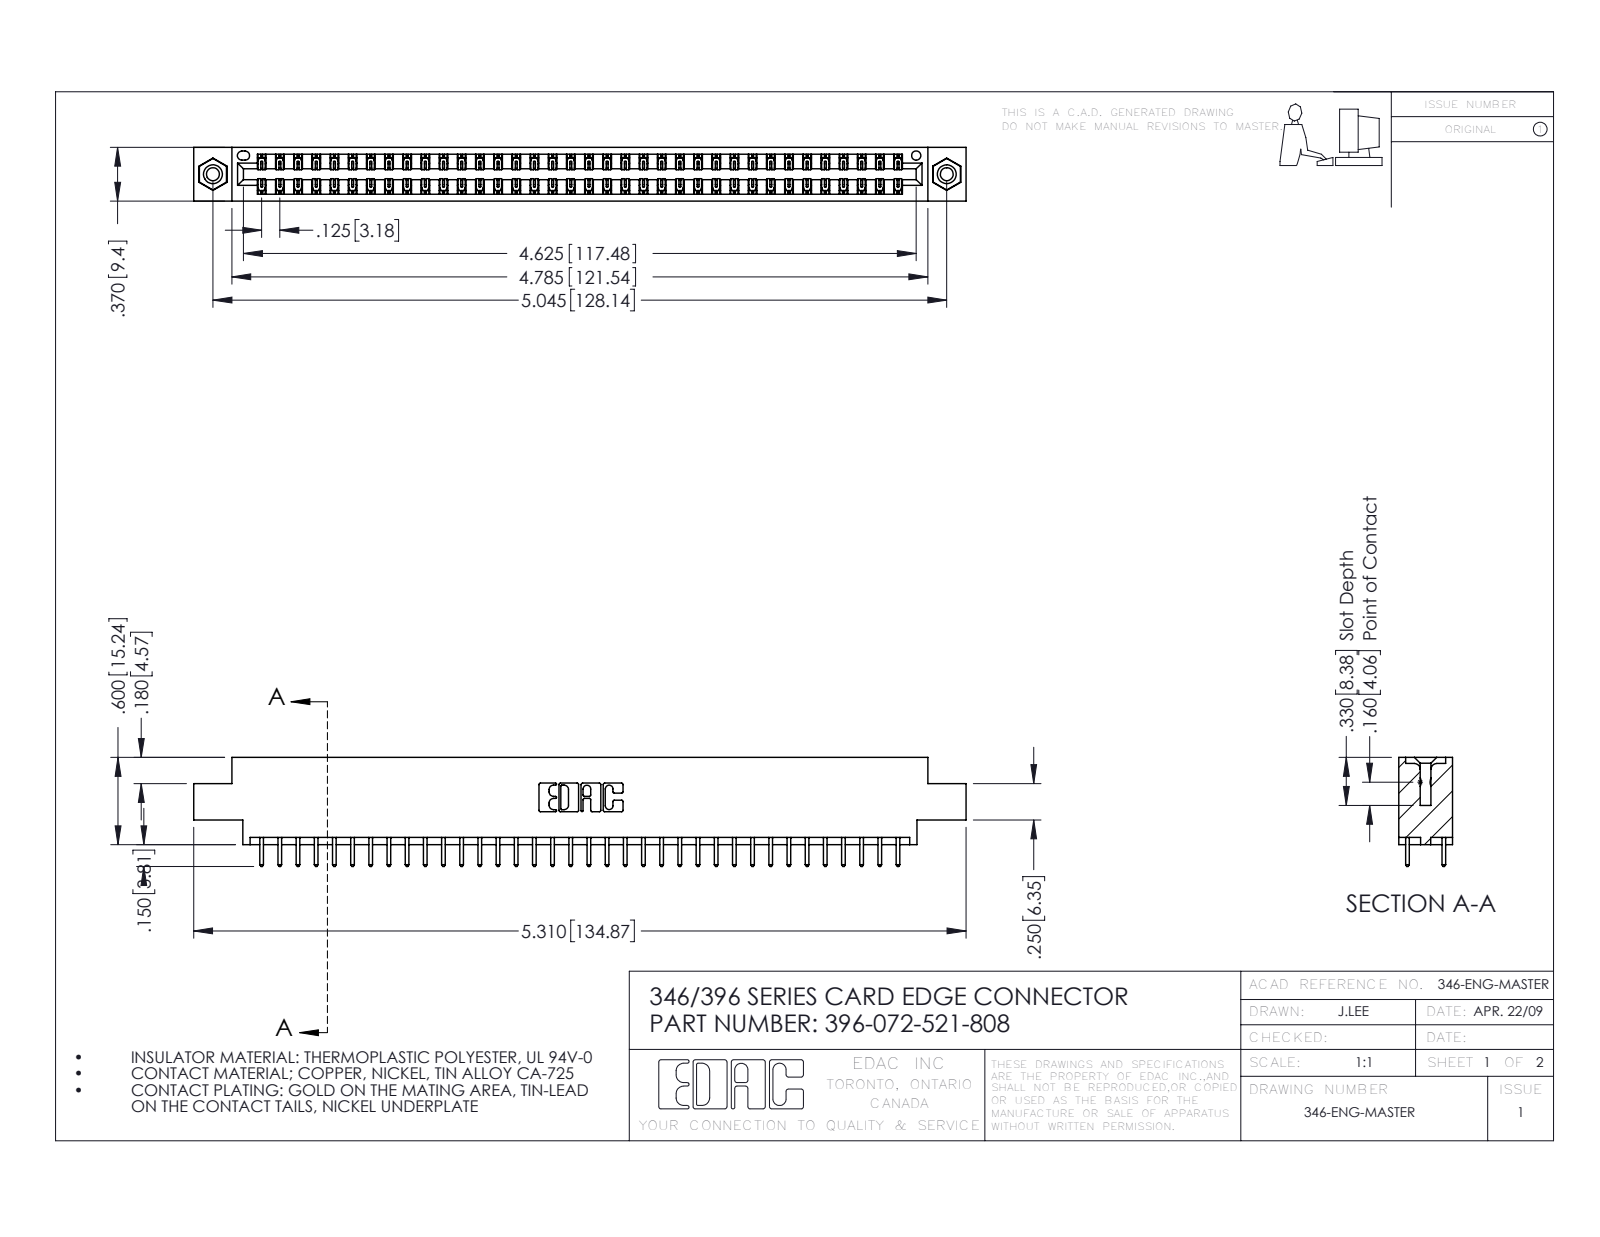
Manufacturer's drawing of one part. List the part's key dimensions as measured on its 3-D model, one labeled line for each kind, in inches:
Part name (STEP PRODUCT): 396-072-521-808; 345-292-001_345-293-121; 345-250-001_345-250-003-102; 346 Part_0.170 Offset - 0.156 Dia-TI
STEP written by: SolidWorks 2016 (CONFIG_CONTROL_DESIGN)
Units: inches
Bodies: 75 solids, 3930 faces (2632 planar, 1282 cylindrical, 16 other)
Overall size (bounding box): 5.31 × 0.75 × 0.37
Volume: 0.788 in³ · Surface area: 27.37 in²
Round holes (diameter × count): ⌀0.089 ×2, ⌀0.125 ×2, ⌀0.156 ×2, ⌀0.064 ×1
Round bosses / shafts (diameter × count): ⌀0.155 ×2
Partial cylindrical surfaces — rounded edges, fillets, slot ends (radius × count): R0.006 ×108, R0.01 ×72, R0.01 ×22, R0.007 ×6, R0.031 ×6, R0.026 ×3, R0.014 ×2, R0.022 ×2
Main face-to-face distances: 0.048, 0.322, 0.37, 0.25, 0.072, 0.298, 0.025, 0.275, 0.222, 0.148
Hole centre spacings: 0.246, 4.836, 5.045
